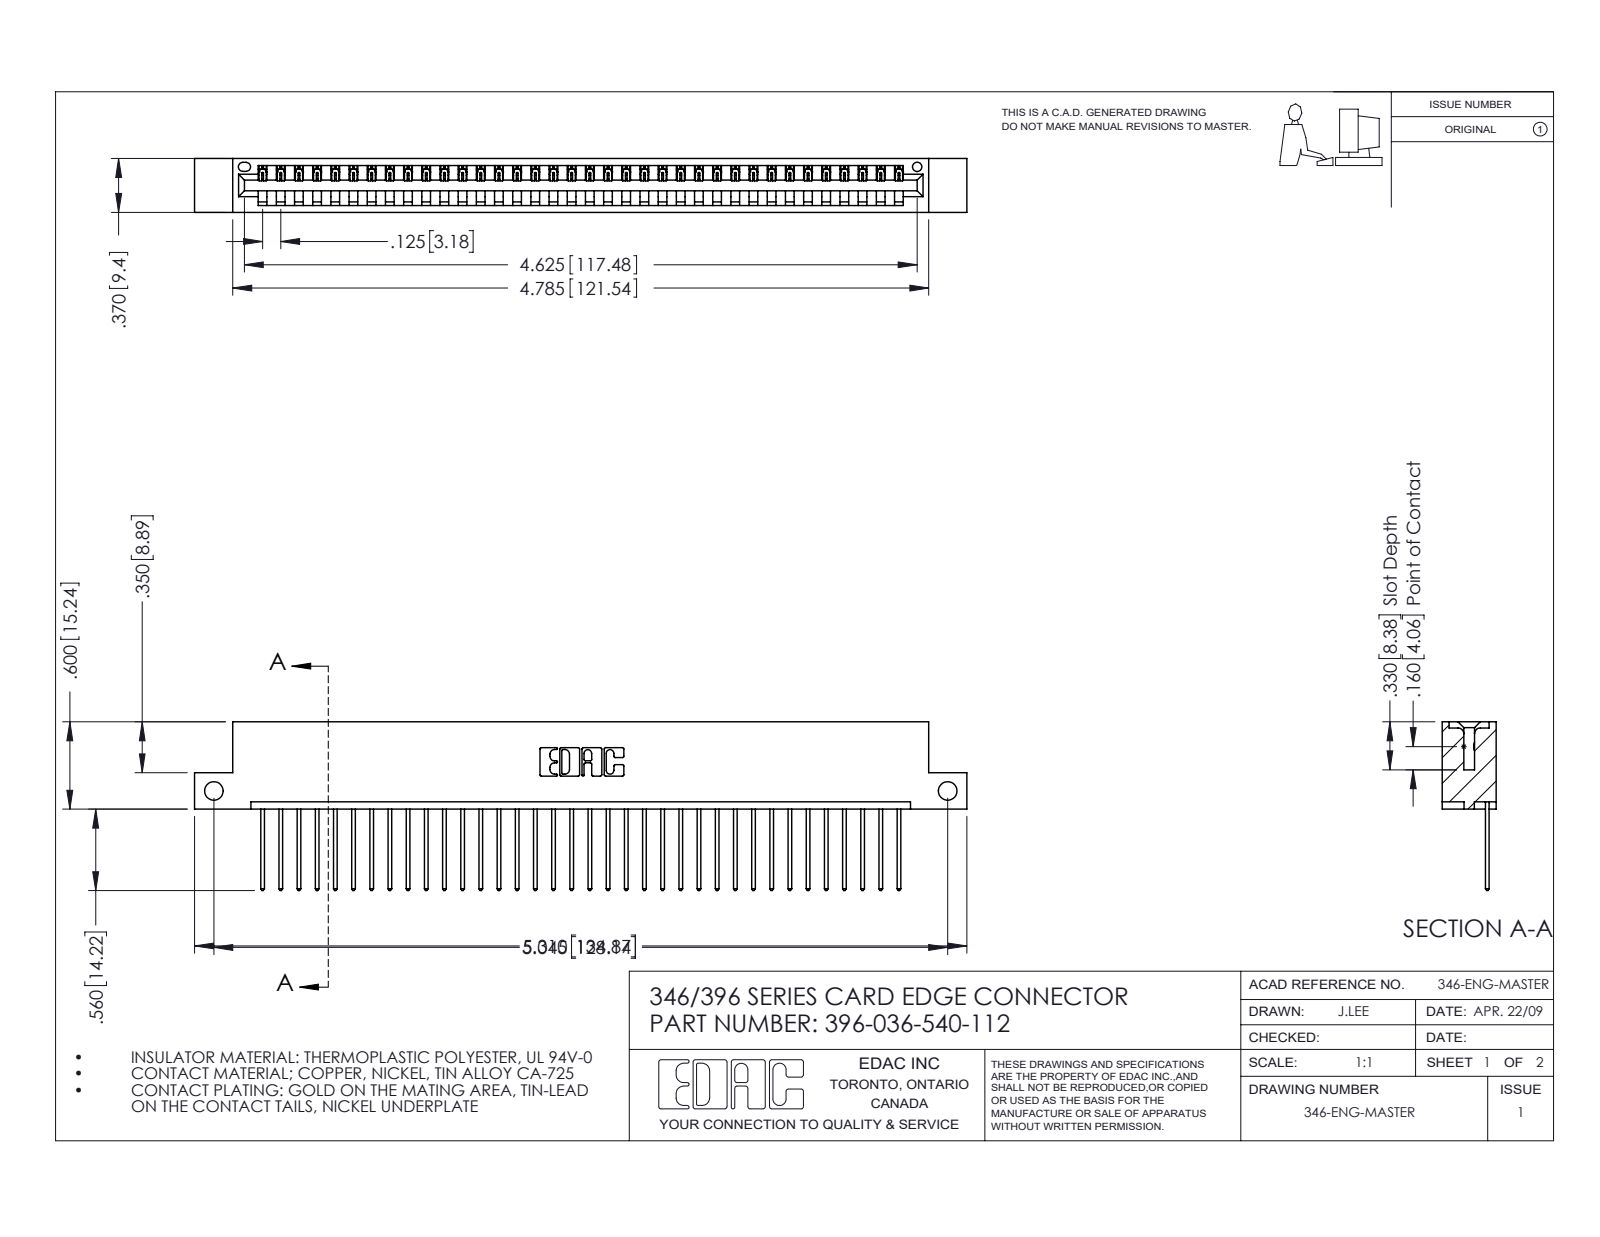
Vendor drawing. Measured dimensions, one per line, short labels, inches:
name: 396-036-540-112; 345-292-001_345-293-140; 346 Part_Flush Mounting Lugs - Side Mount
written by: SolidWorks 2016 (CONFIG_CONTROL_DESIGN)
unit: in
bodies: 37 solids, 2210 faces (1516 planar, 694 cylindrical, 0 other)
size: 5.31 × 1.16 × 0.37
volume: 0.783 in³; area: 25.08 in²
holes: 2× ⌀0.128, 1× ⌀0.064
rounds: 72× R0.006, 72× R0.01, 22× R0.01, 6× R0.007, 6× R0.031, 3× R0.026, 2× R0.031, 2× R0.04
face distances: 0.048, 0.322, 0.37, 0.25, 0.072, 0.298, 0.025, 0.148, 0.222, 0.1
hole spacings: 5.045
